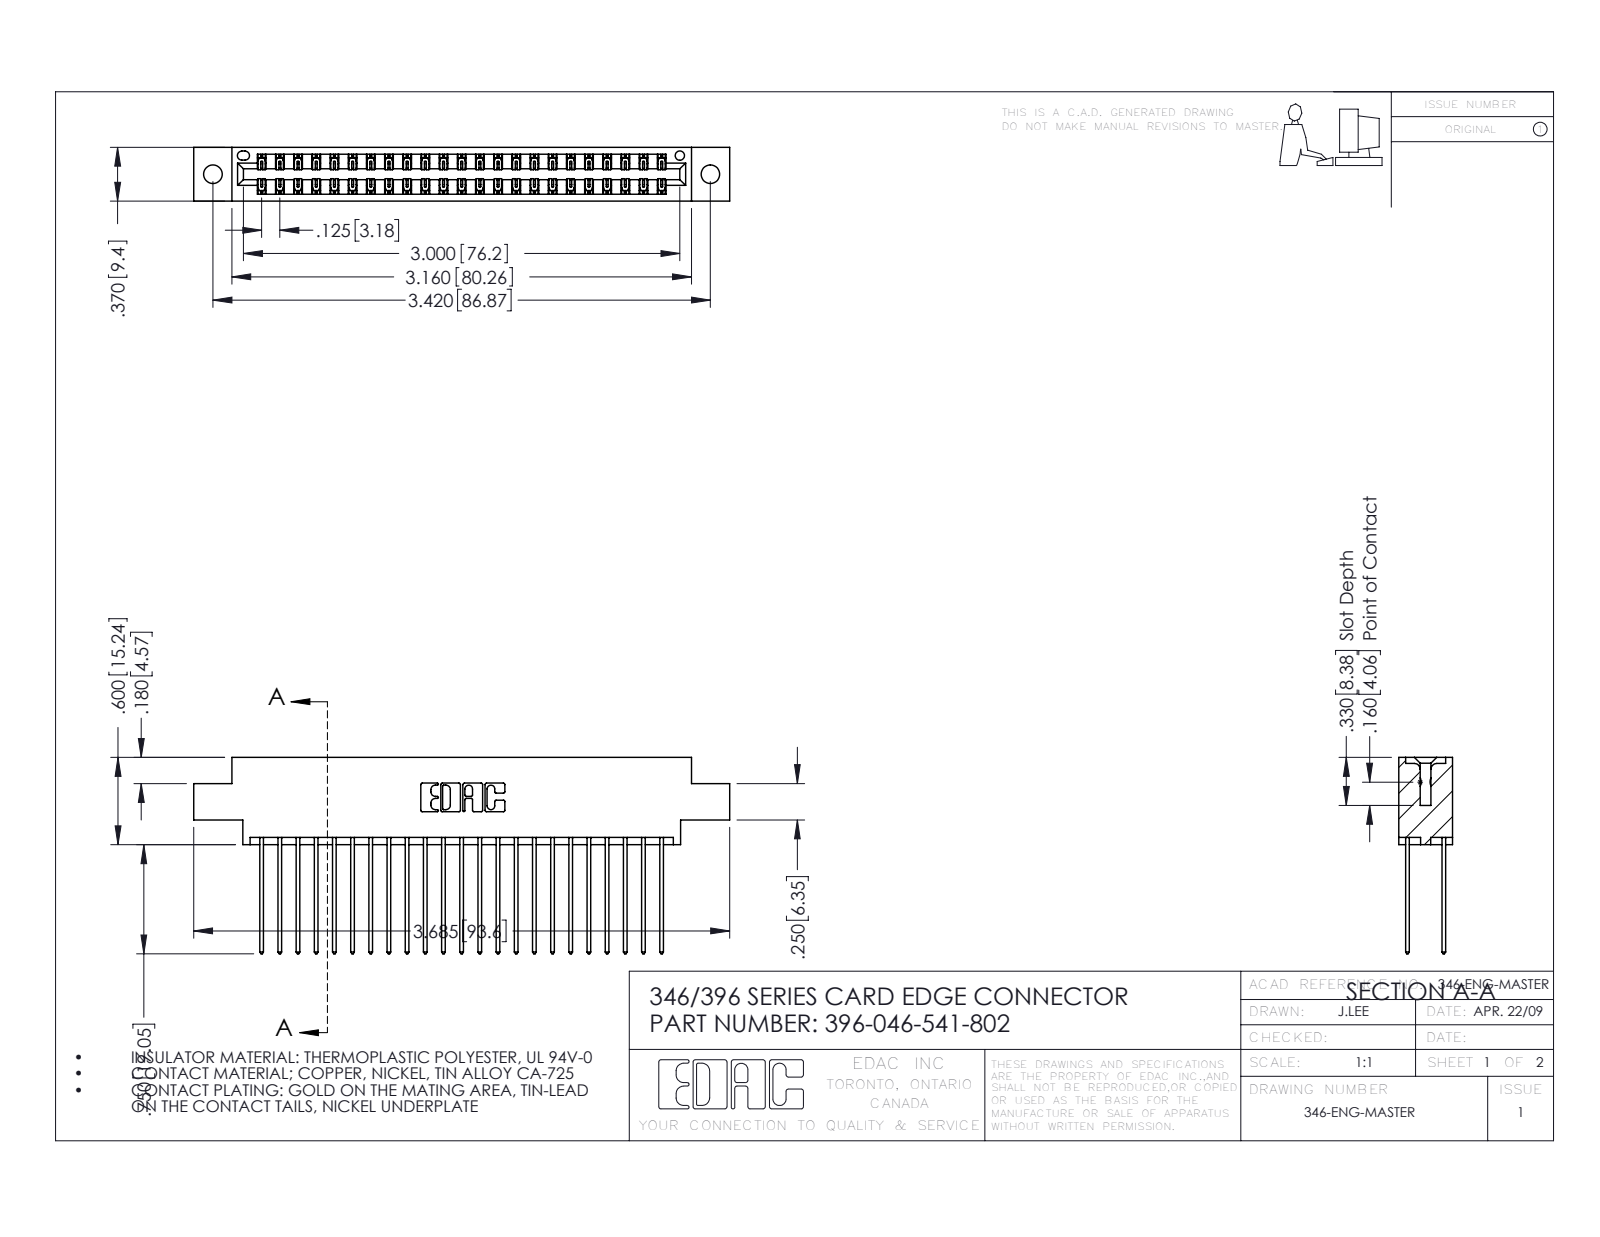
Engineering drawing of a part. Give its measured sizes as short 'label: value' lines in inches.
name: 346 Part_0.170 Offset - 0.128 Dia; 345-292-001_345-293-141; 396-046-541-802
written by: SolidWorks 2016 (CONFIG_CONTROL_DESIGN)
unit: in
bodies: 47 solids, 2518 faces (1690 planar, 828 cylindrical, 0 other)
size: 3.685 × 1.35 × 0.37
volume: 0.552 in³; area: 20.65 in²
holes: 2× ⌀0.128, 1× ⌀0.064
rounds: 69× R0.006, 46× R0.01, 22× R0.01, 6× R0.007, 6× R0.031, 3× R0.026, 2× R0.014, 2× R0.022
face distances: 0.048, 0.322, 0.25, 0.072, 0.298, 0.025, 0.37, 0.275, 0.225, 0.148
hole spacings: 0.246, 3.212, 3.42
